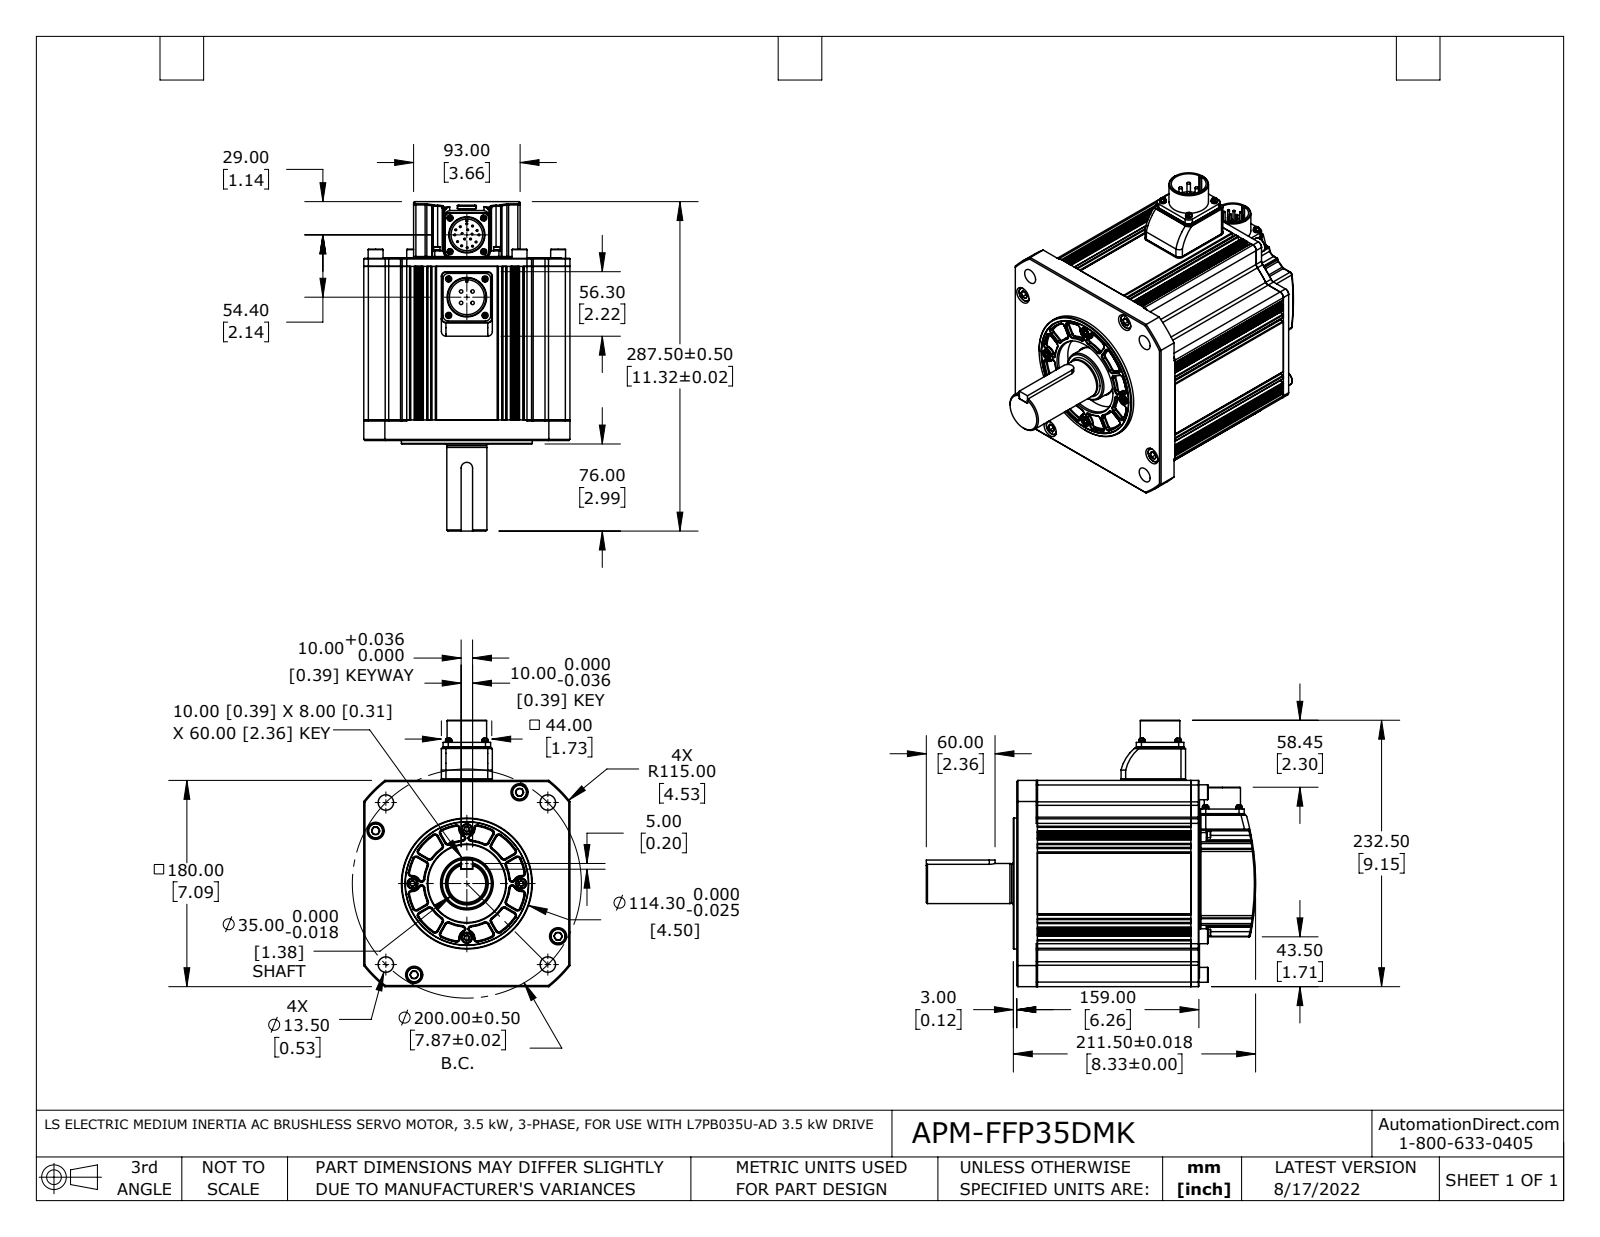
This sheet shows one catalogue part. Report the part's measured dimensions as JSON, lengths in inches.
{"part_name": "FMP18GA001G02_Out Line(APM-FFP35D_K) r1 nc fxt", "step_written_by": "SolidWorks 2017 (AUTOMOTIVE_DESIGN)", "units": "inches", "bodies": {"solids": 57, "faces": 2335, "planar": 784, "cylindrical": 864, "other": 687}, "overall_size": [11.319, 9.154, 7.087], "volume_in3": 305.8, "surface_area_in2": 736.9, "round_holes": [[0.118, 13], [0.098, 9], [0.12, 8], [0.236, 8], [0.374, 8], [0.138, 4], [0.142, 4], [0.146, 4], [0.197, 4], [0.268, 4], [0.354, 4], [0.362, 4]], "round_bosses_or_shafts": [[0.063, 17], [0.213, 8], [0.52, 4], [0.512, 4], [0.335, 4], [0.315, 4], [0.217, 4], [0.118, 4]], "partial_cylinders_radius": [[0.02, 124], [0.098, 56], [0.157, 24], [0.079, 17], [0.039, 14], [0.177, 12], [0.256, 4], [0.012, 2]], "face_to_face_distances": [5.276, 0.039, 0.709, 0.295, 0.394, 0.315, 7.087, 0.276, 5.591, 5.61], "hole_center_spacings": [1.282, 2.93, 5.423, 0.042, 0.819, 0.885, 0.927, 1.035]}
